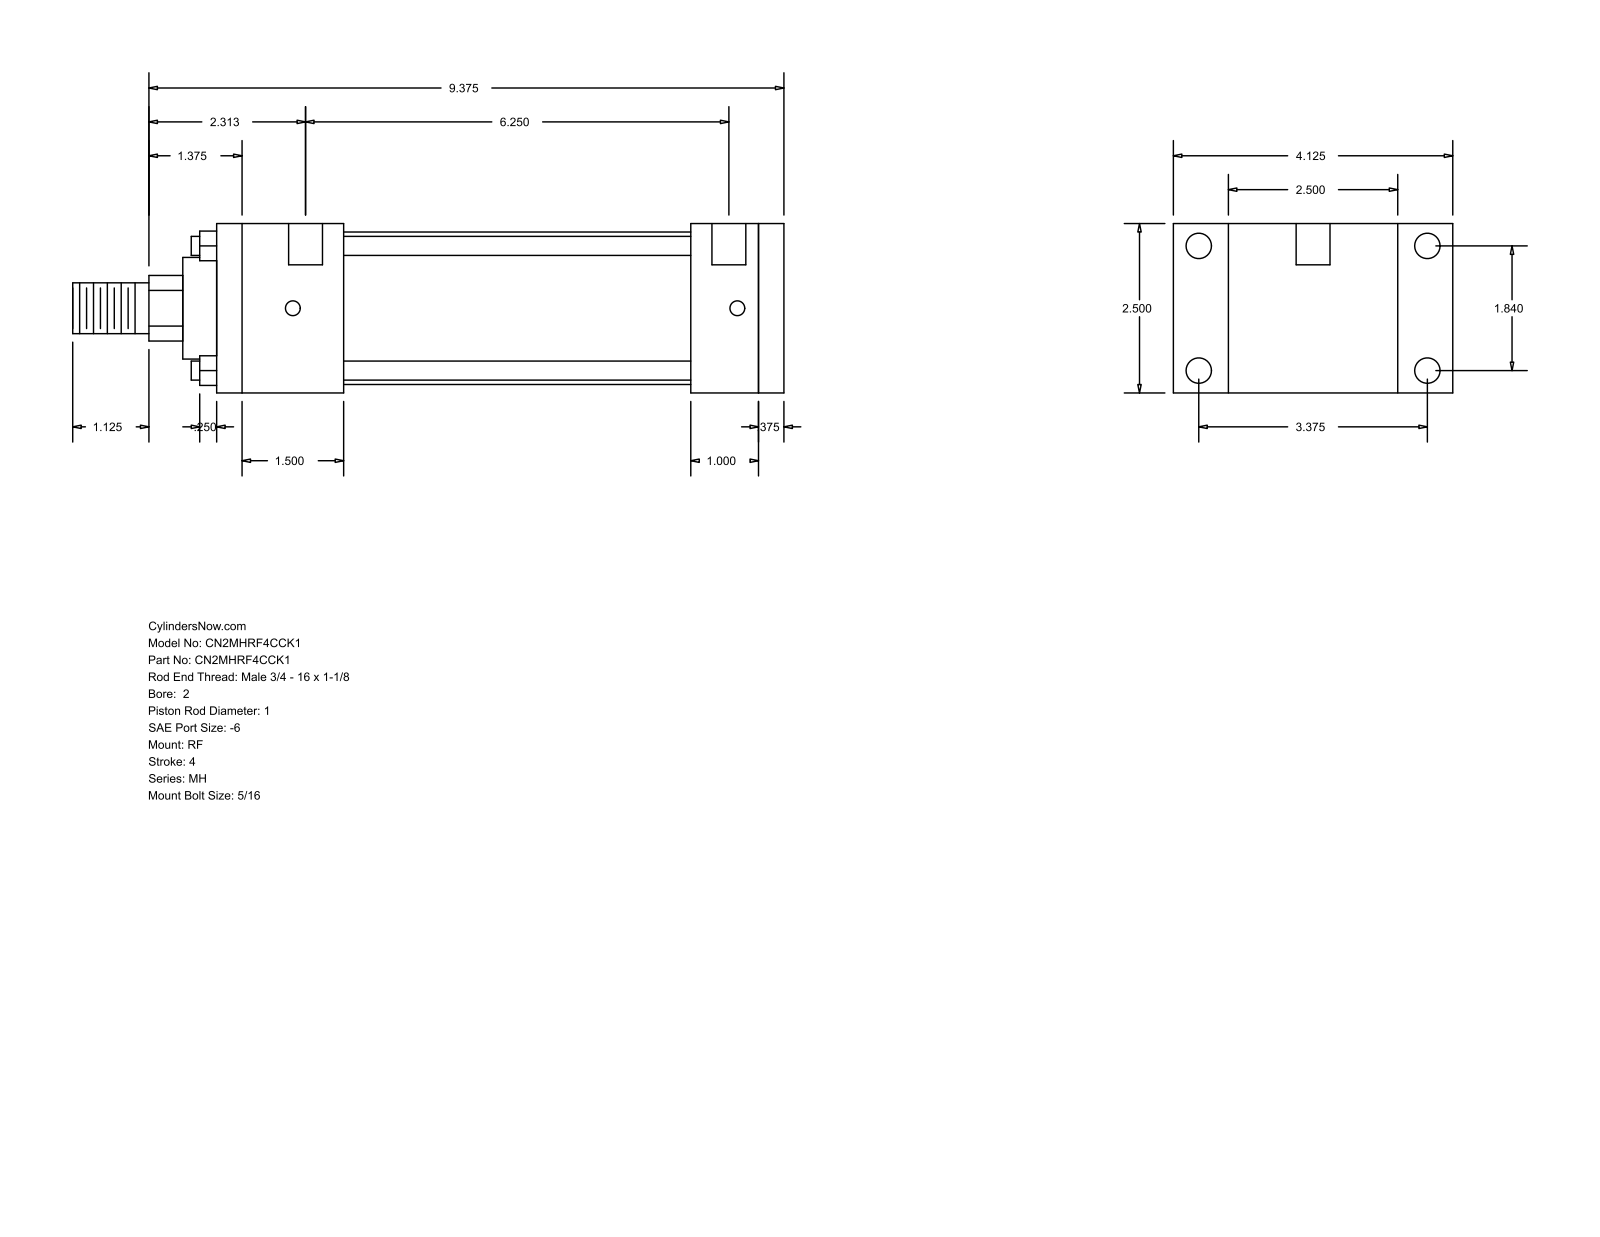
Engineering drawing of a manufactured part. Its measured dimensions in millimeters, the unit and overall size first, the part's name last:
Units: millimetres
Overall size (bounding box): 266.7 × 104.78 × 63.5
Round holes (diameter × count): ⌀5.56 ×4, ⌀9.53 ×4, ⌀12.7 ×2
Round bosses / shafts (diameter × count): ⌀7.14 ×4, ⌀57.15 ×1, ⌀38.1 ×1, ⌀25.4 ×1, ⌀19.05 ×1
Partial cylindrical surfaces — rounded edges, fillets, slot ends (radius × count): R12.29 ×1
Main face-to-face distances: 63.5, 212.72, 9.52, 203.2, 20.64, 25.4, 47.63, 177.8, 130.17, 155.57
Hole centre spacings: 46.74, 85.72, 97.63, 166.68, 3.17, 4.76, 158.75, 161.92
Bodies: 0 solids, 92 faces (64 planar, 28 cylindrical, 0 other)
Part name (STEP PRODUCT): MH_RF__0200_1
STEP written by: GSSL Pune (CONFIG_CONTROL_DESIGN)
